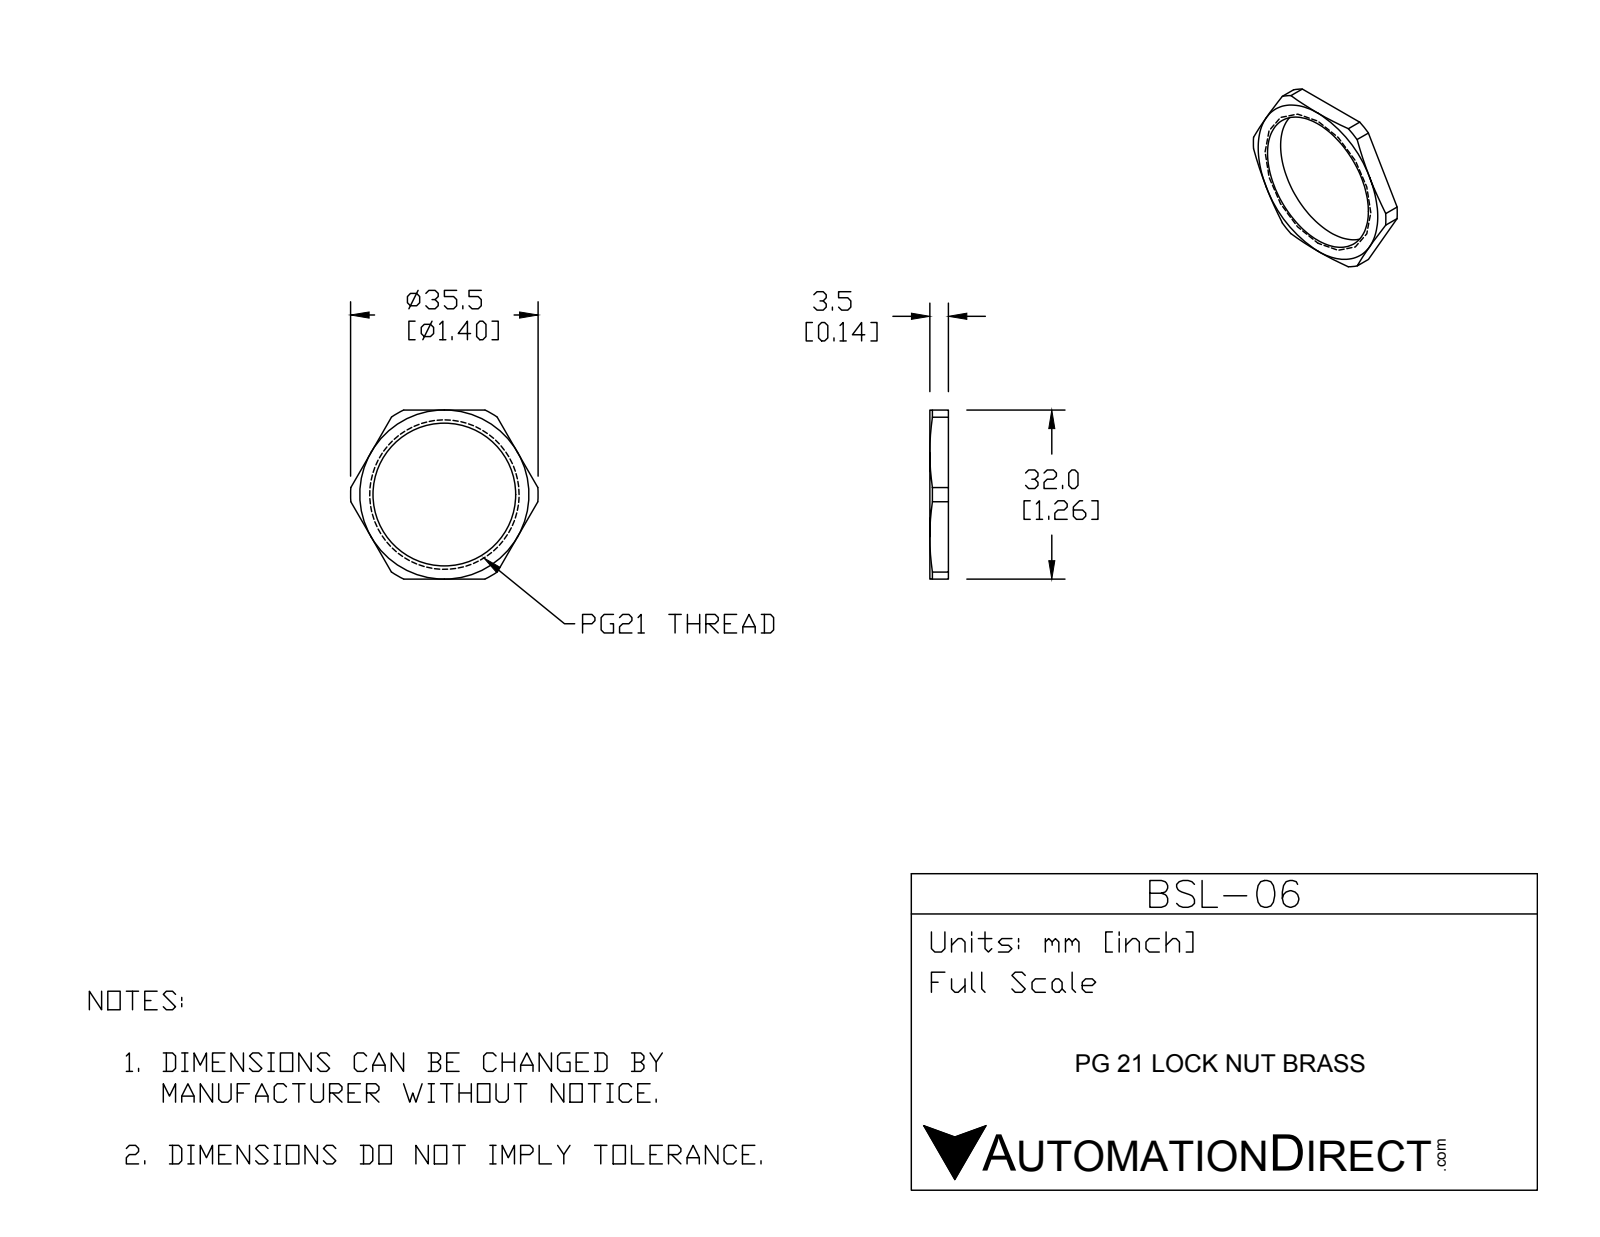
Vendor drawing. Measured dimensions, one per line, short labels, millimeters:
name: BSL-06
written by: SolidWorks 2015 (CONFIG_CONTROL_DESIGN)
unit: mm
bodies: 1 solid, 23 faces (8 planar, 9 cylindrical, 6 other)
size: 35.5 × 32 × 3.5
volume: 1 066 mm³; area: 1 274 mm²
holes: 1× ⌀27
rounds: 1× R17.75
face distances: 3.5, 32
